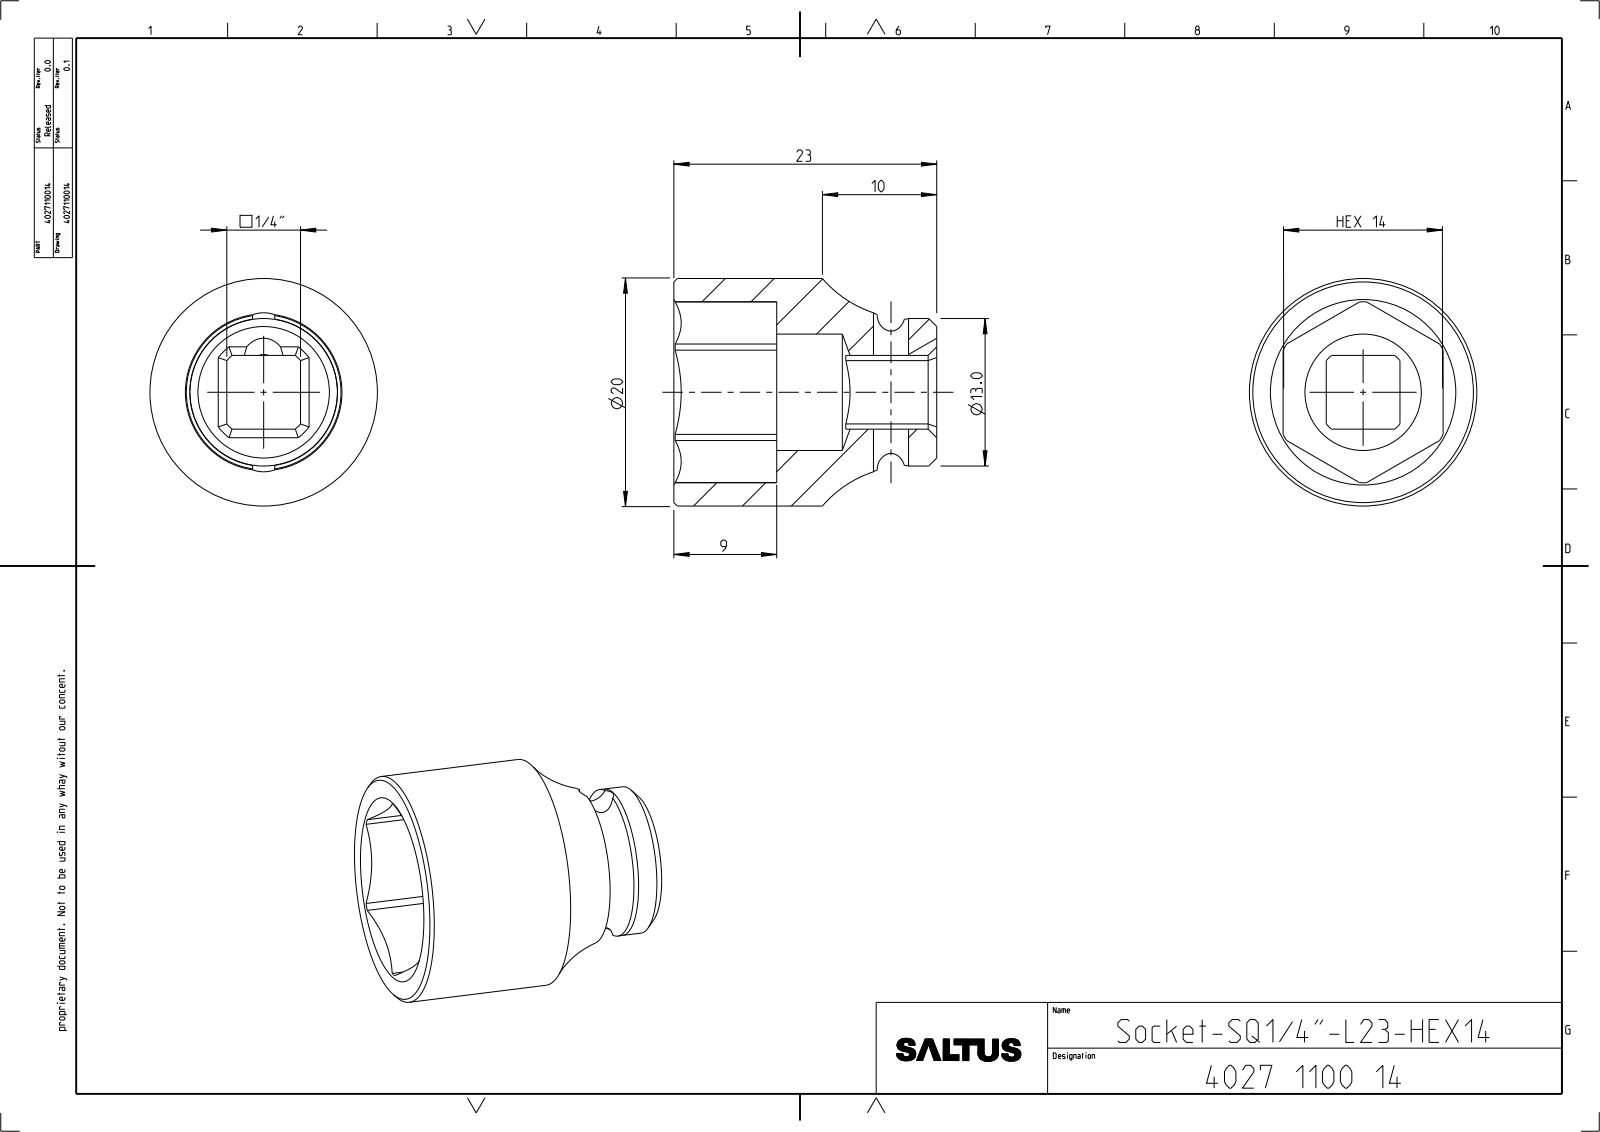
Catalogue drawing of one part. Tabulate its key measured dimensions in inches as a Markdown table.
| quantity | value |
| --- | --- |
| part name | 4027110014 |
| STEP written by | CREO PARAMETRIC BY PTC INC, 2022414 (CONFIG_CONTROL_DESIGN) |
| units | inches |
| bodies | 1 solid, 59 faces (20 planar, 21 cylindrical, 18 other) |
| overall size | 0.906 × 0.783 × 0.783 |
| volume | 0.198 in³ |
| surface area | 3.864 in² |
| round holes (diameter × count) | 0.121 × 1, 0.401 × 1 |
| round bosses / shafts (diameter × count) | 0.783 × 1, 0.508 × 1 |
| partial cylindrical surfaces (radius × count) | 0.079 × 1, 0.167 × 1, 0.311 × 1 |
| main face-to-face distances | 0.551, 0.354, 0.148, 0.403, 0.254, 0.906, 0.205, 0.346, 0.701 |
